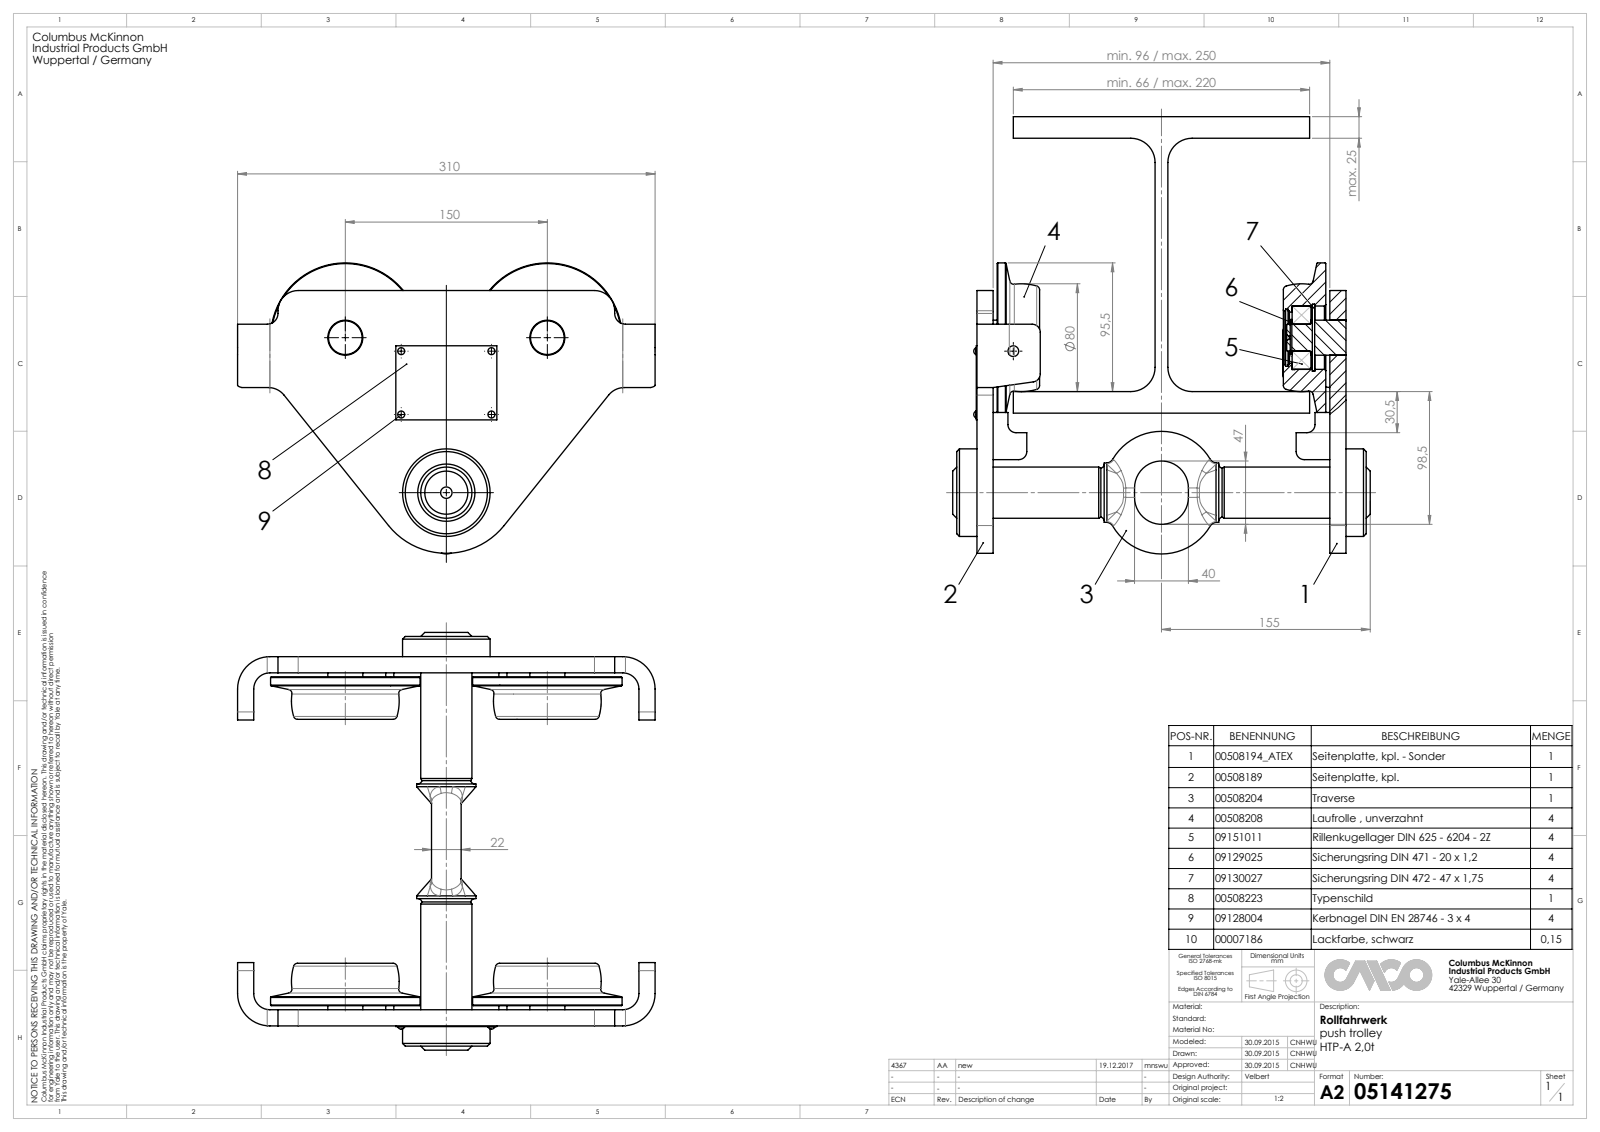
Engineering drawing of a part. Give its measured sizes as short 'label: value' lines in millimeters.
name: HTP-A 2,0t
written by: SolidWorks 2015 (AUTOMOTIVE_DESIGN)
unit: mm
bodies: 35 solids, 816 faces (236 planar, 340 cylindrical, 240 other)
size: 500 × 324.5 × 310
volume: 6 660 000 mm³; area: 1 090 000 mm²
holes: 10× ⌀2, 8× ⌀2.5, 4× ⌀3, 4× ⌀3.5, 2× ⌀8, 2× ⌀19, 2× ⌀26, 2× ⌀36.71, 2× ⌀38, 2× ⌀40, 2× ⌀42.5, 2× ⌀47
bosses: 4× ⌀5.2, 2× ⌀111, 2× ⌀49.5, 2× ⌀26.99, 2× ⌀20, 1× ⌀65, 1× ⌀44, 1× ⌀38
rounds: 8× R2, 8× R2.5, 8× R6, 4× R12, 4× R15, 4× R18, 4× R24, 2× R8
face distances: 16, 204, 220, 12, 188, 132.25, 141.75, 9.5, 262, 120.25
hole spacings: 11.49, 21.55, 150, 5, 6.25, 10.13, 11.57, 16.24
